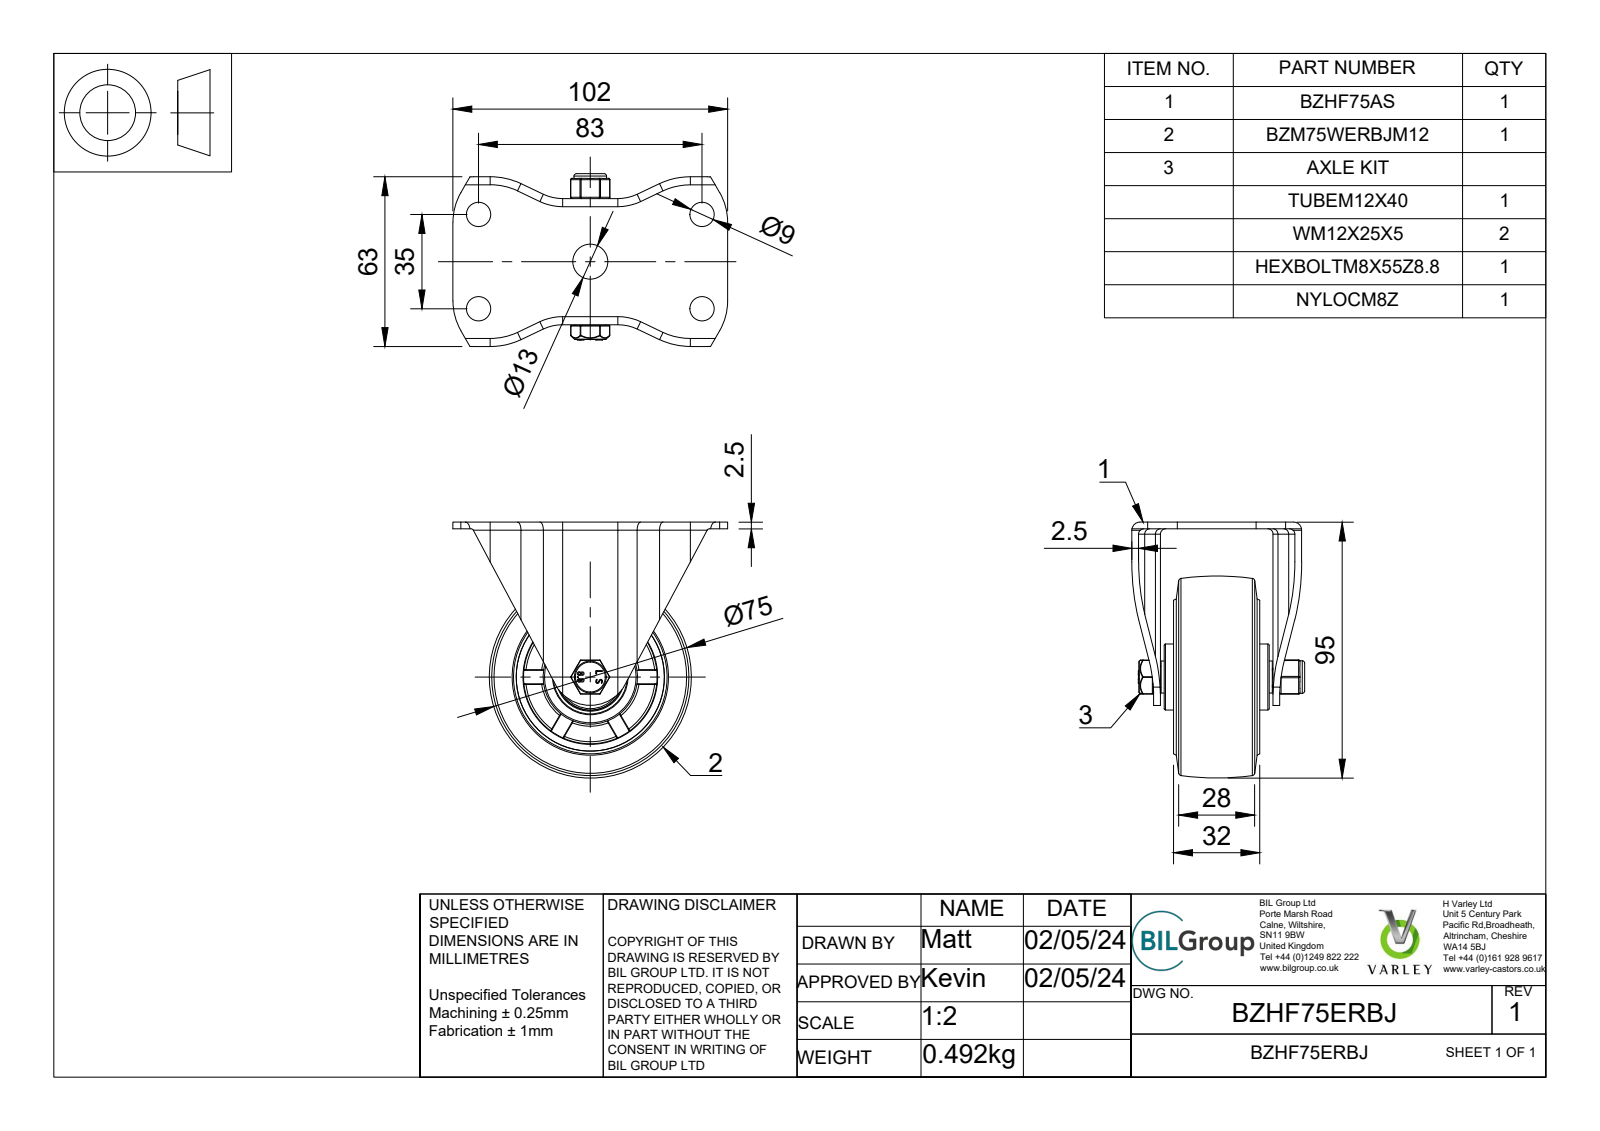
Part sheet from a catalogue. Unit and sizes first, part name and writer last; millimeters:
Units: millimetres
Overall size (bounding box): 102 × 95 × 64.15
Round holes (diameter × count): ⌀9 ×4, ⌀0.66 ×2, ⌀8 ×1, ⌀8.2 ×1, ⌀8.4 ×1, ⌀8.6 ×1, ⌀12 ×1, ⌀12.75 ×1, ⌀13 ×1, ⌀17 ×1, ⌀17.5 ×1, ⌀17.75 ×1
Round bosses / shafts (diameter × count): ⌀35 ×1, ⌀24.5 ×1, ⌀18 ×1, ⌀16 ×1, ⌀15.5 ×1, ⌀12.1 ×1, ⌀11.9 ×1, ⌀11.5 ×1
Partial cylindrical surfaces — rounded edges, fillets, slot ends (radius × count): R0.25 ×35, R0.5 ×18, R2 ×8, R3 ×8, R0.33 ×4, R0.64 ×4, R17 ×4, R19.5 ×4
Main face-to-face distances: 2.5, 44.3, 35.4, 8.9, 37.9, 6.4, 13.5, 46.8, 30.5, 22.4
Hole centre spacings: 45.04, 3.21, 35, 83, 90.08, 2.49
Volume: 131 077 mm³ · Surface area: 81 029 mm²
Bodies: 36 solids, 893 faces (210 planar, 307 cylindrical, 376 other)
Part name (STEP PRODUCT): BZHF75ERBJ v3; BZHF75AS v1; ZINC PLATED, PRESSED STEEL BRACKET; BZM75WERBJM12 v1 (+7 more)
STEP written by: Autodesk Translation Framework v12.20.1.177 (AUTOMOTIVE_DESIGN)
